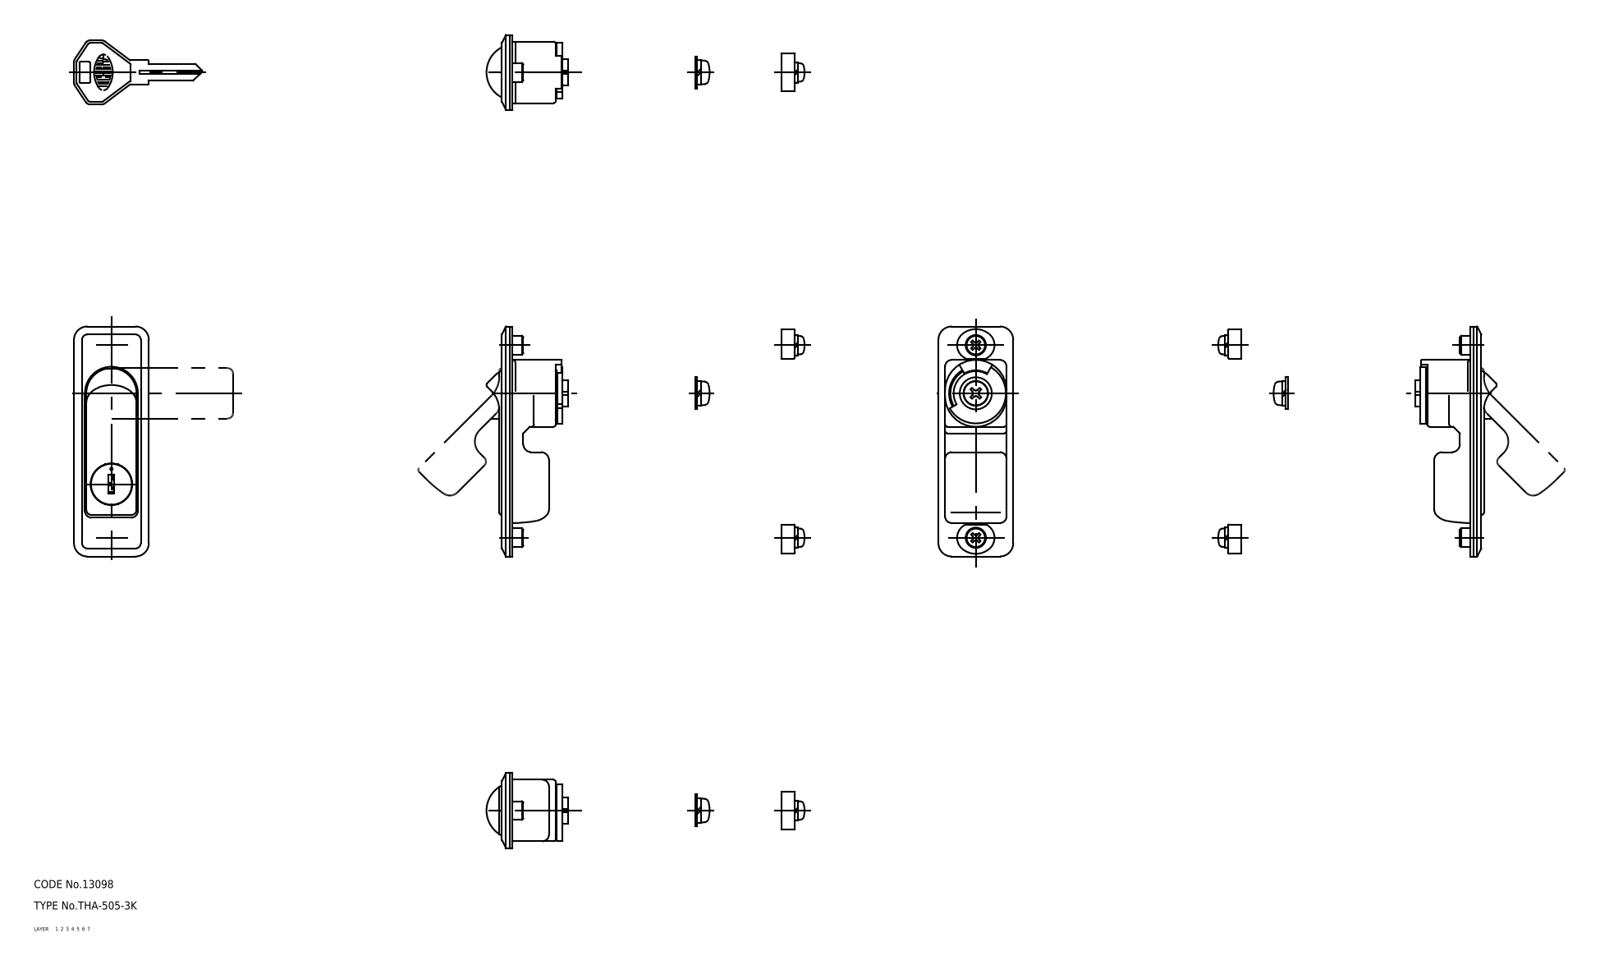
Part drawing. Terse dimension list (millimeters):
name: lock; key; screw_B; bracket (+8 more)
written by: CADfix (AUTOMOTIVE_DESIGN)
unit: mm
bodies: 13 solids, 437 faces (0 planar, 0 cylindrical, 437 other)
size: 93.93 × 86 × 28
volume: 25 977 mm³; area: 23 384 mm²
